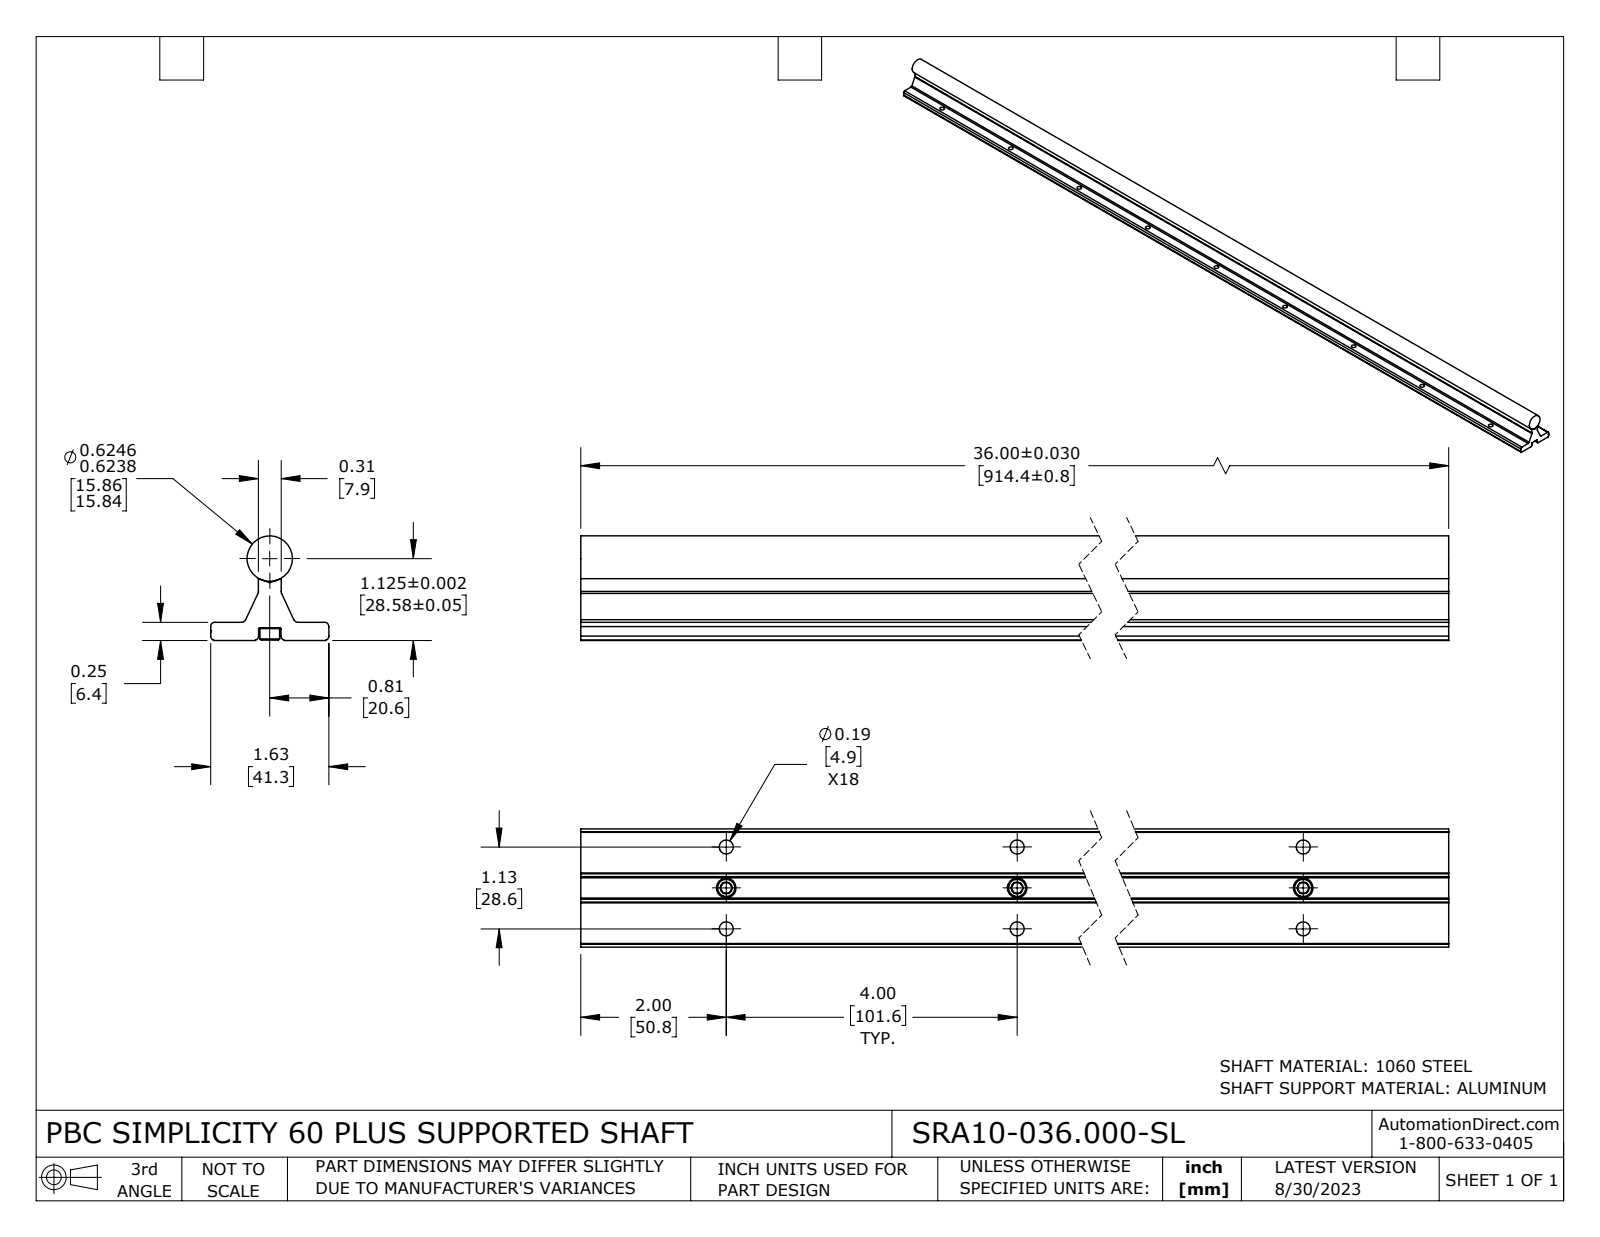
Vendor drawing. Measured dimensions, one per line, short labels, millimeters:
name: SRA10-036.000-SL
written by: SolidWorks 2021 (CONFIG_CONTROL_DESIGN)
unit: mm
bodies: 11 solids, 401 faces (126 planar, 140 cylindrical, 135 other)
size: 914.4 × 41.3 × 36.5
volume: 535 400 mm³; area: 167 900 mm²
holes: 27× ⌀4.9, 9× ⌀3.6, 9× ⌀4.8
bosses: 9× ⌀6.9, 9× ⌀4.2, 1× ⌀15.9
rounds: 6× R1.5, 2× R0.4, 2× R1.6, 2× R1.6
face distances: 6.4, 4.4, 1.9, 16.7, 24.6, 16.7, 24.6, 7.9, 8, 41.3
hole spacings: 102.6, 203.7, 101.6, 305.1, 203.2, 406.7, 14.3, 304.8
